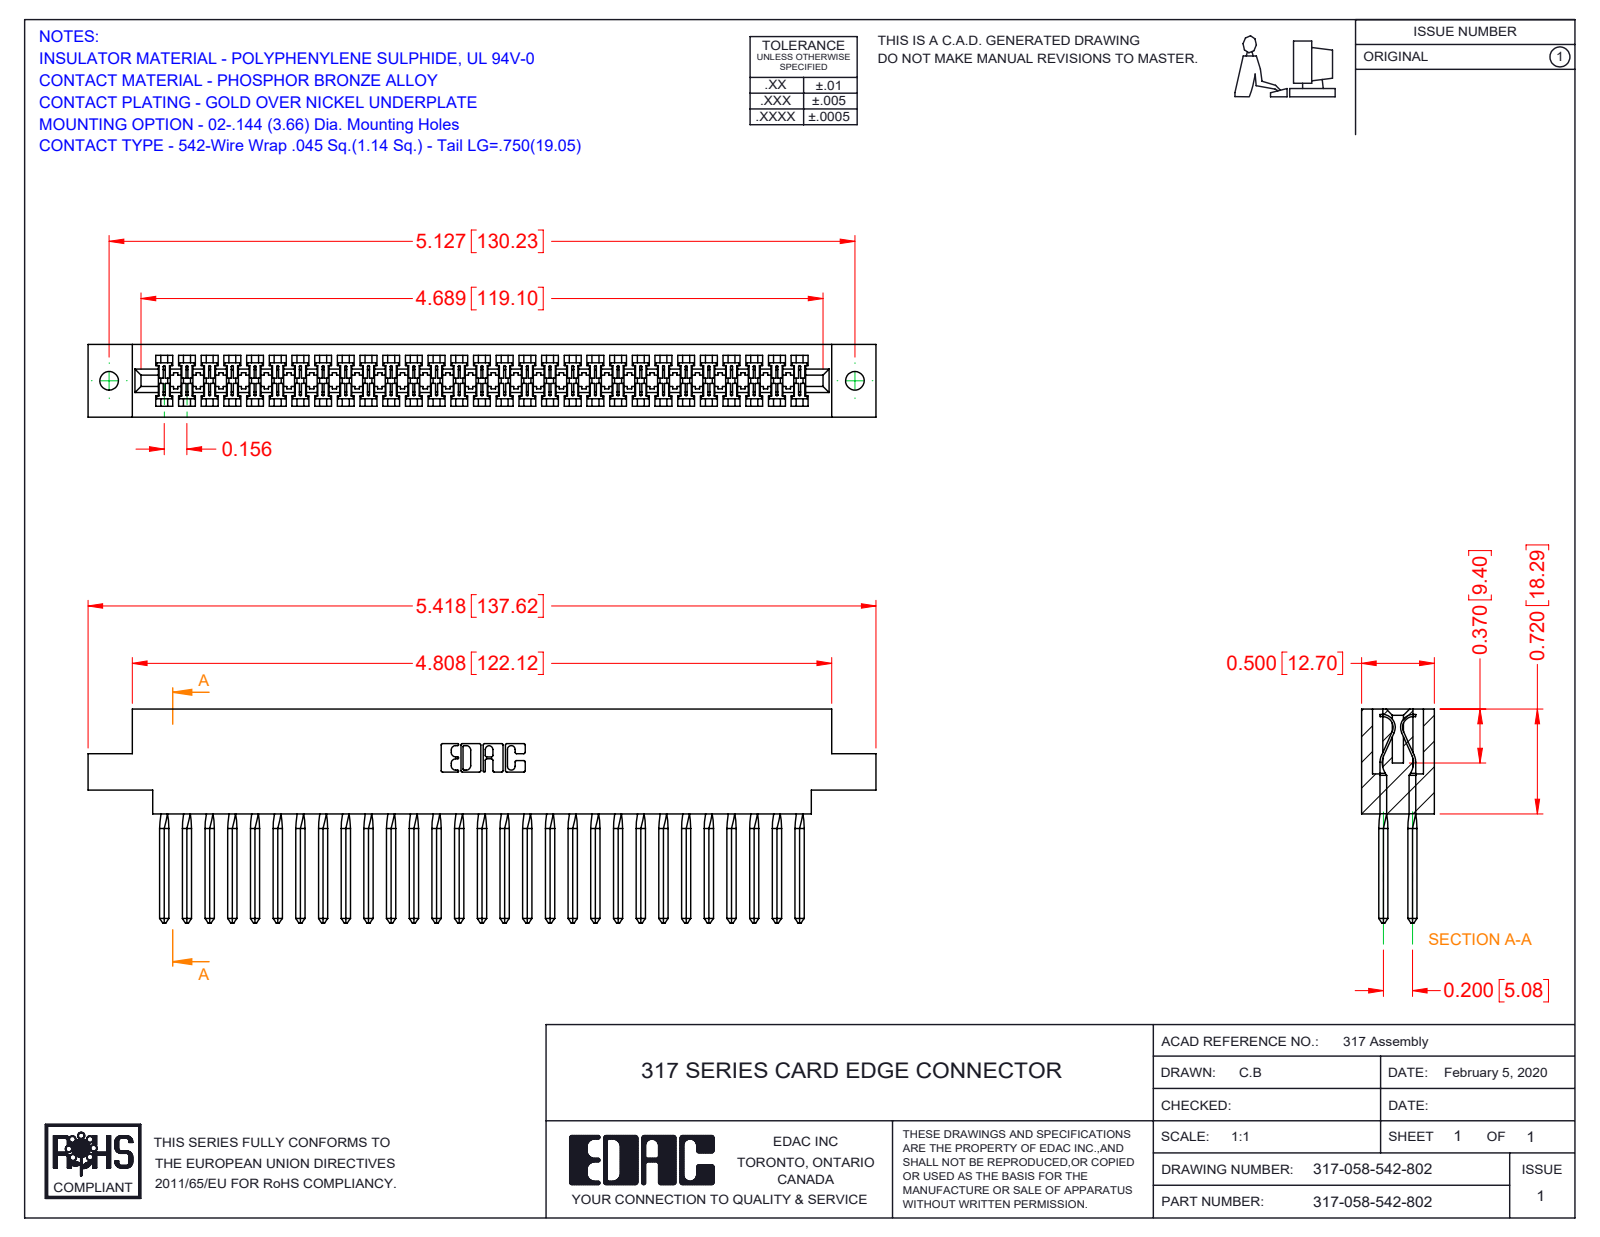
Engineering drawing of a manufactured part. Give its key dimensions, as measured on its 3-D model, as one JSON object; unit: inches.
{"part_name": "317-290-003_542; 317-058-542-802; 317 Part_.144 Dia", "step_written_by": "SolidWorks 2016 (CONFIG_CONTROL_DESIGN)", "units": "inches", "bodies": {"solids": 59, "faces": 3408, "planar": 2726, "cylindrical": 450, "other": 232}, "overall_size": [5.418, 1.47, 0.5], "volume_in3": 1.348, "surface_area_in2": 46.55, "round_holes": [[0.128, 2]], "partial_cylinders_radius": [[0.006, 116], [0.01, 22], [0.007, 6], [0.031, 6], [0.026, 3], [0.074, 2], [0.089, 2], [0.1, 2]], "face_to_face_distances": [0.5, 0.075, 0.425, 0.35, 0.2, 0.11, 0.046, 0.116, 0.128, 0.372], "hole_center_spacings": [5.127]}
